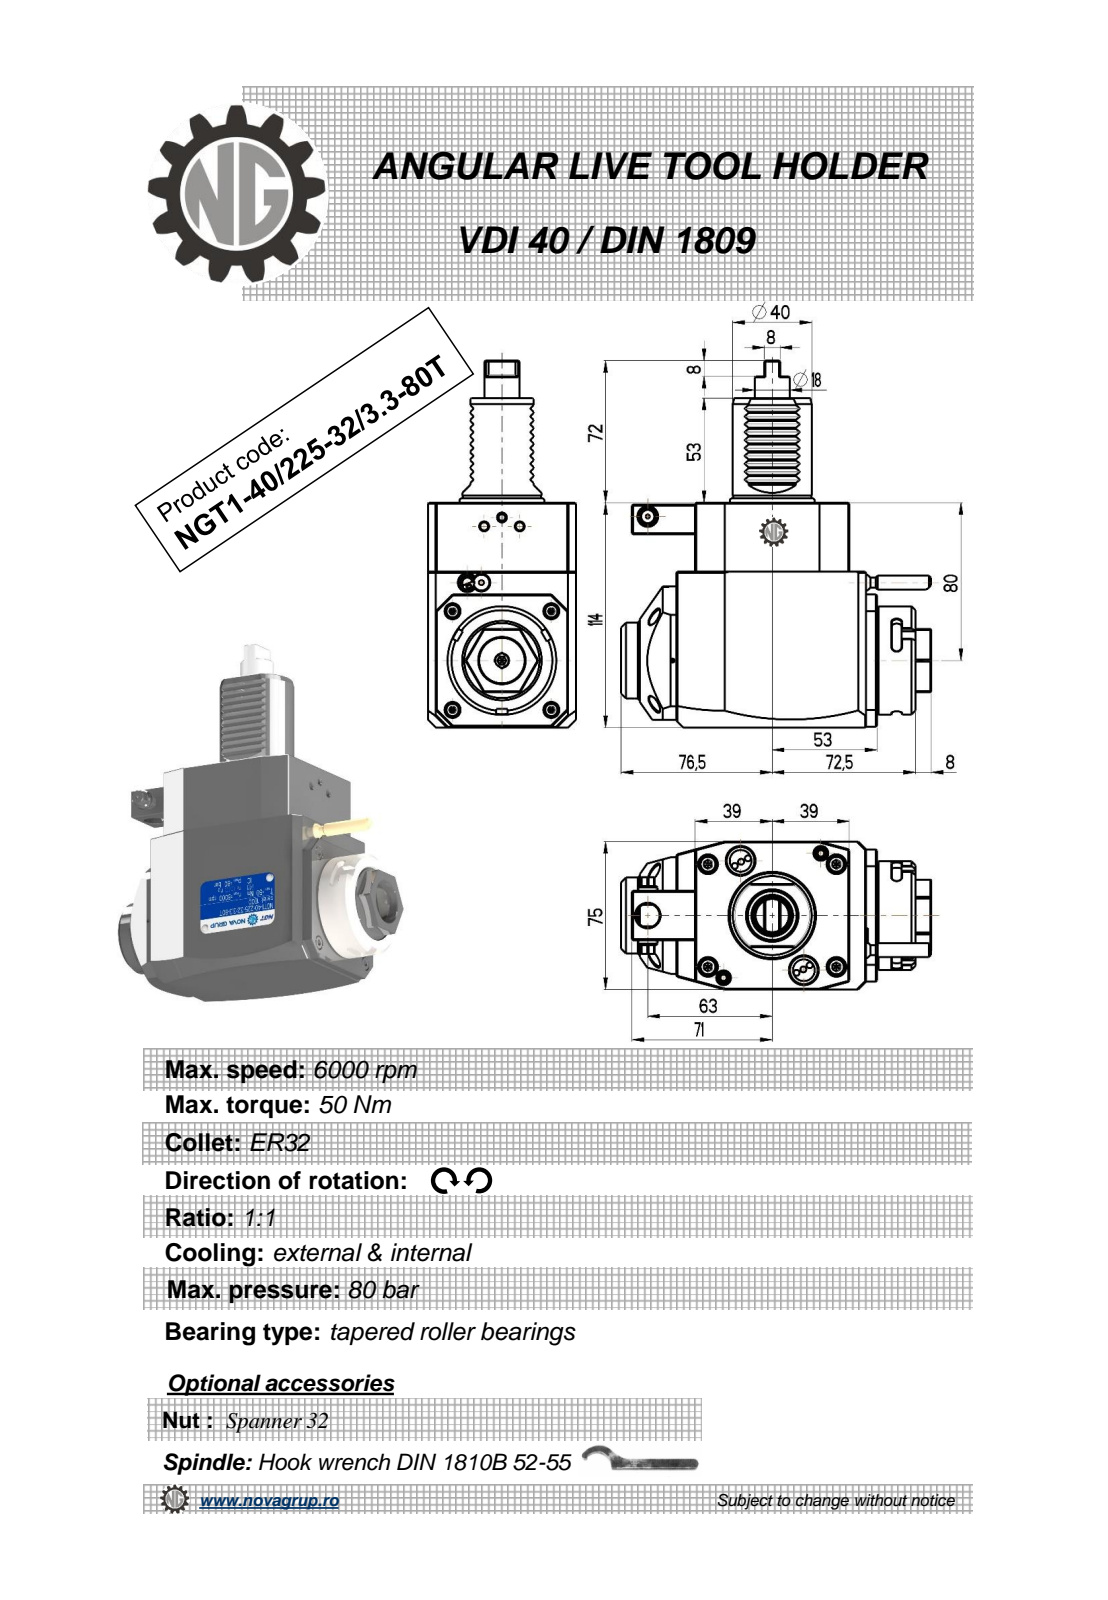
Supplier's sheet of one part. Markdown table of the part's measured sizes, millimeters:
| quantity | value |
| --- | --- |
| part name | NGT1_40_225_32_3_3_80T |
| STEP written by | PRO/ENGINEER BY PARAMETRIC TECHNOLOGY CORPORATION, 2010280 (CONFIG_CONTROL_DESIGN) |
| units | millimeters |
| bodies | 1 solid, 403 faces (228 planar, 95 cylindrical, 80 other) |
| overall size | 186 × 157 × 75 |
| volume | 962 130 mm³ |
| surface area | 72 577 mm² |
| round holes (diameter × count) | 2 × 1, 2.5 × 1, 3 × 1, 4.5 × 1, 9.5 × 1, 12 × 1, 23 × 1 |
| round bosses / shafts (diameter × count) | 8 × 2, 55 × 1, 48 × 1, 40 × 1, 38.5 × 1, 17.8 × 1, 10 × 1, 7 × 1 |
| partial cylindrical surfaces (radius × count) | 0.3 × 20, 2.5 × 6, 0.8 × 2, 180 × 2, 3.85 × 1, 4.25 × 1, 24.5 × 1, 37.5 × 1 |
| main face-to-face distances | 75, 114, 14, 78, 92, 25, 111.5, 33.5, 19.5, 35 |
| hole center spacings | 37.35, 43.2, 72.5 |
